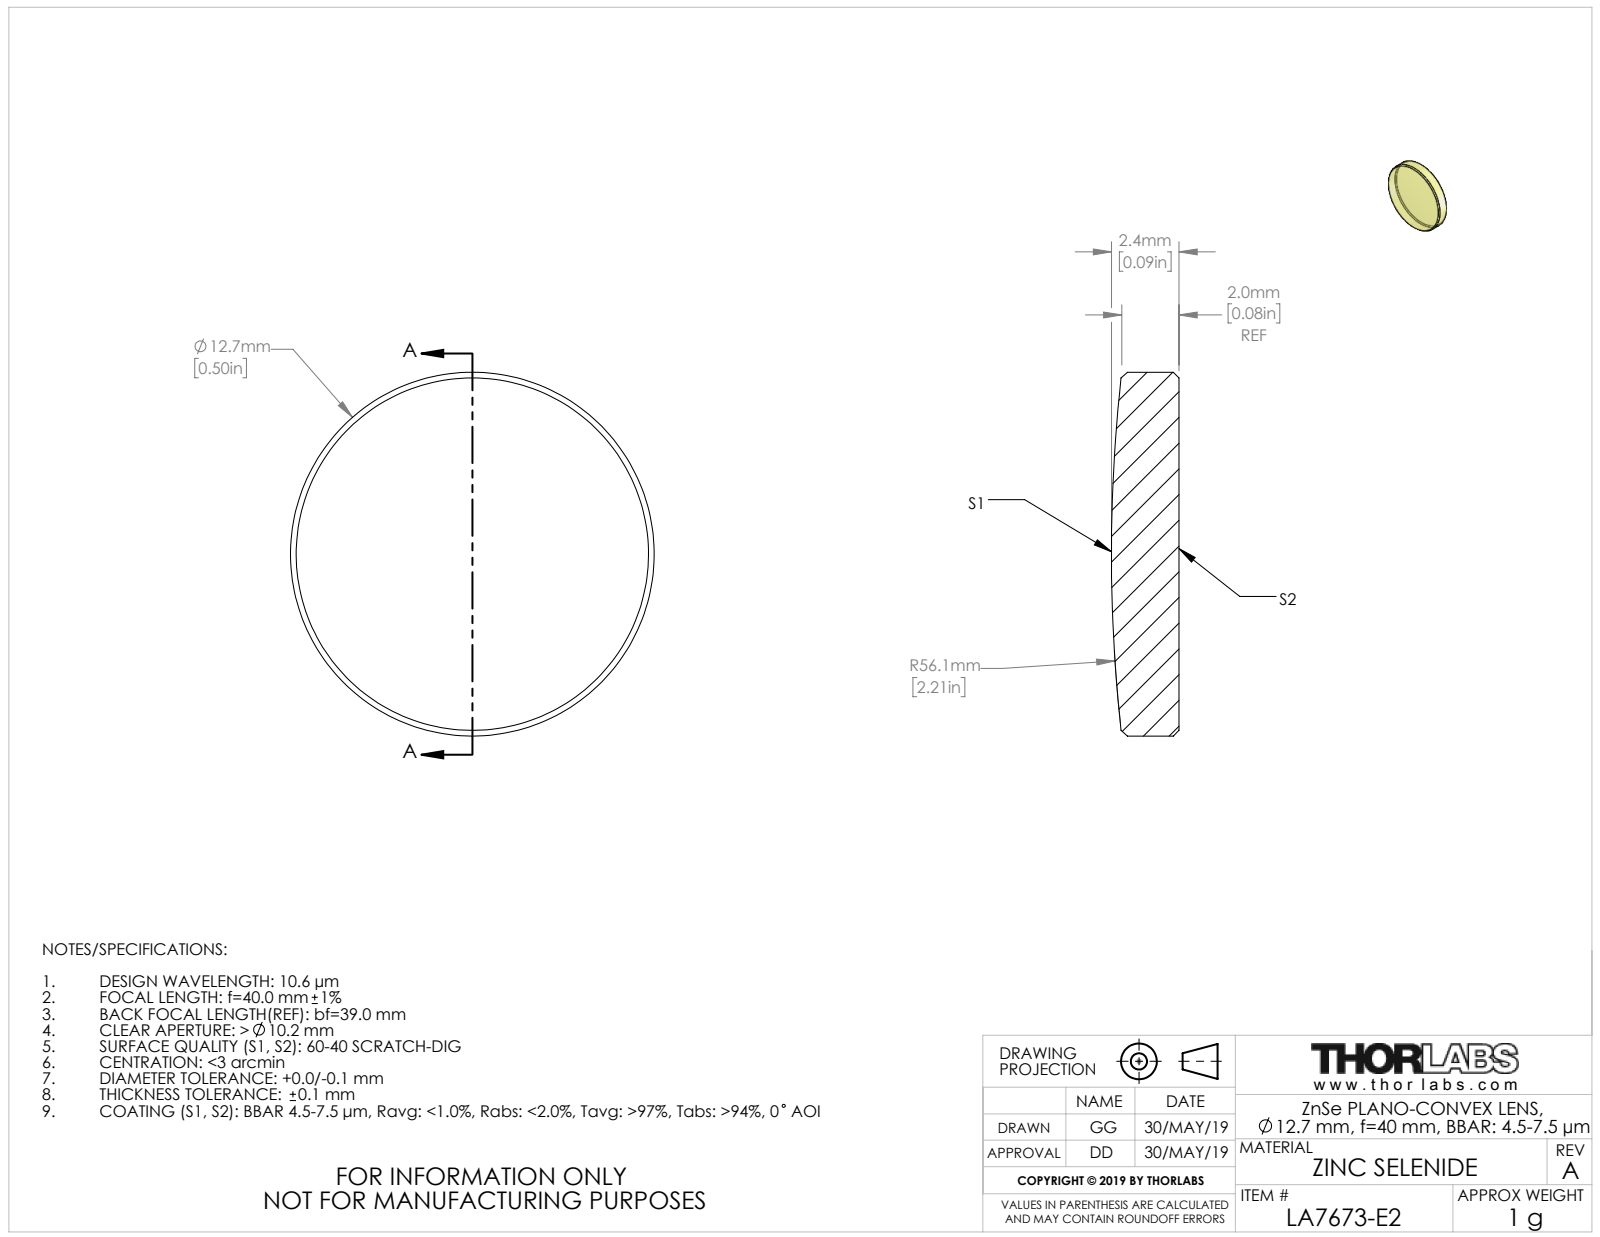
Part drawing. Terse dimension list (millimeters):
name: TTN047581-E0W
written by: SolidWorks 2018 (CONFIG_CONTROL_DESIGN)
unit: mm
bodies: 1 solid, 9 faces (1 planar, 2 cylindrical, 6 other)
size: 12.7 × 12.7 × 2.36
volume: 275 mm³; area: 325 mm²
bosses: 1× ⌀12.7
